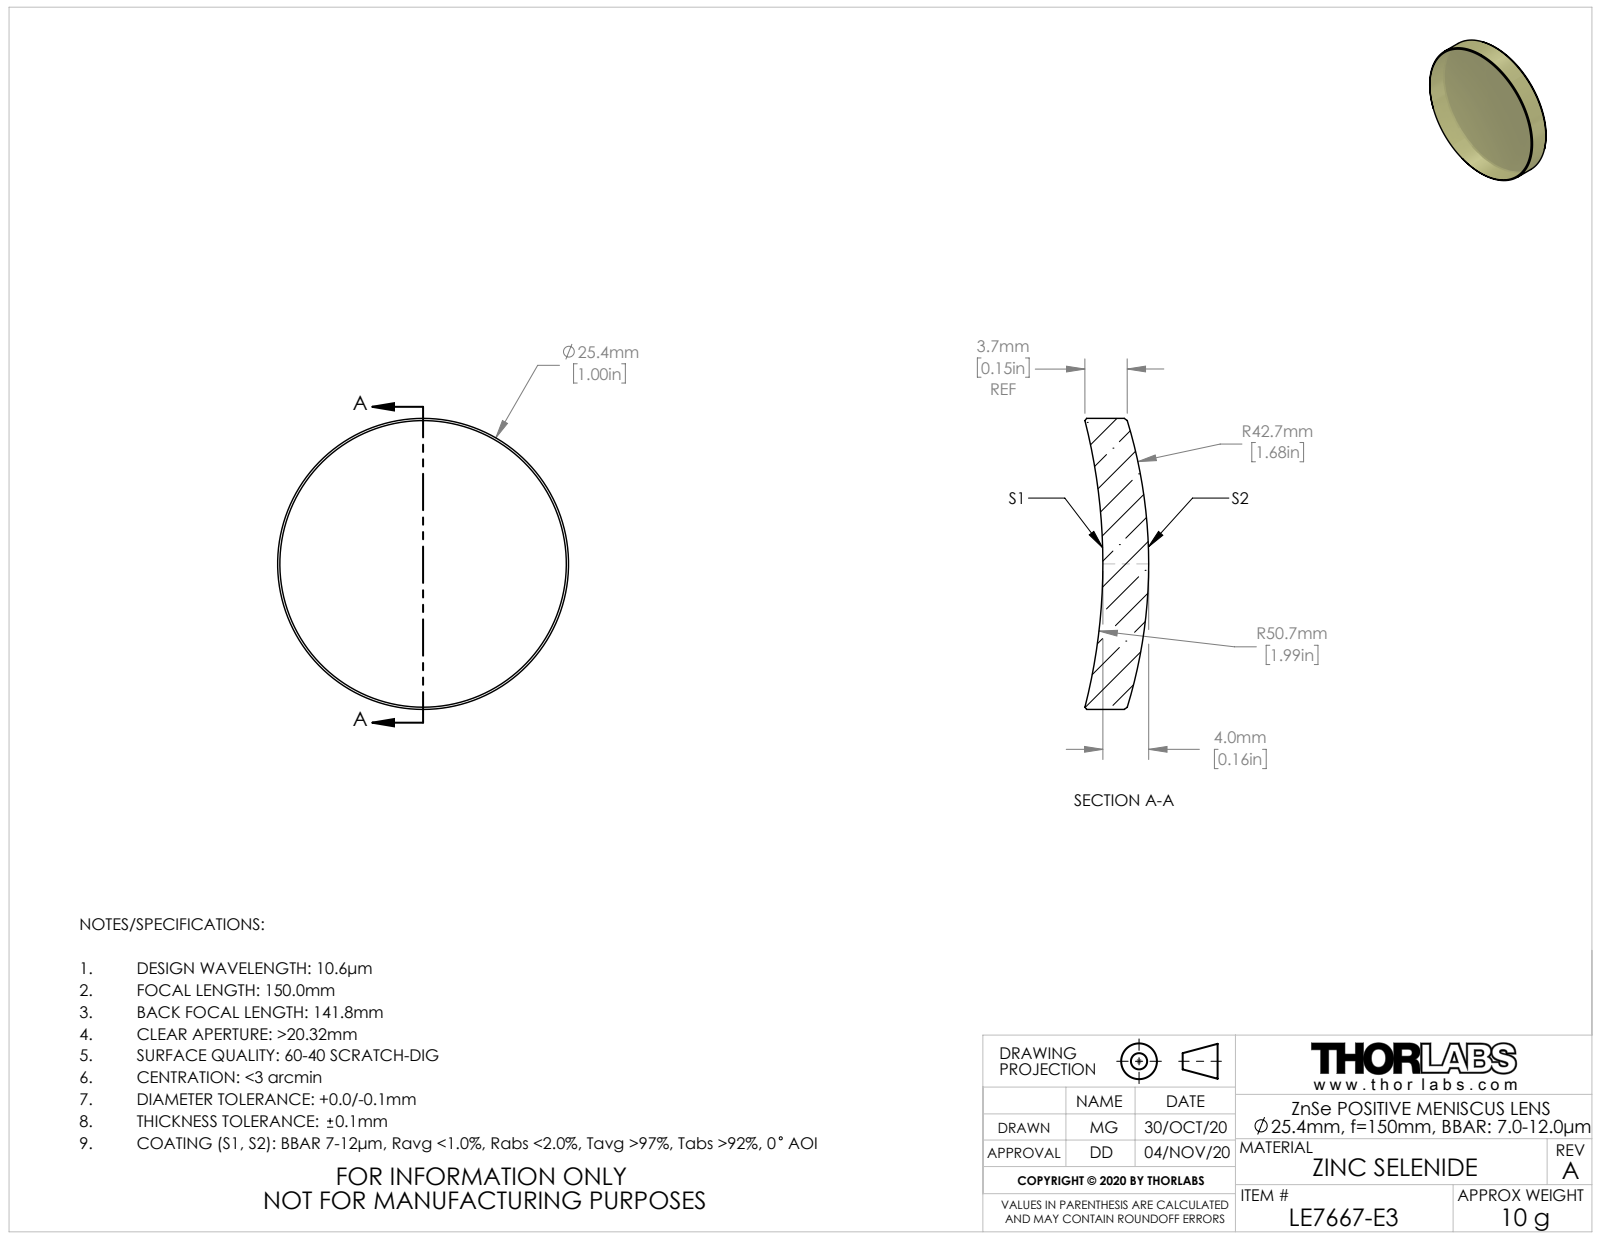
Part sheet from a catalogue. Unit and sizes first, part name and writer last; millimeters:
Units: millimetres
Overall size (bounding box): 25.4 × 25.4 × 5.57
Round bosses / shafts (diameter × count): ⌀25.4 ×1
Volume: 1 946 mm³ · Surface area: 1 309 mm²
Bodies: 1 solid, 10 faces (0 planar, 2 cylindrical, 8 other)
Part name (STEP PRODUCT): TTN225631-E0W
STEP written by: SolidWorks 2018 (CONFIG_CONTROL_DESIGN)
